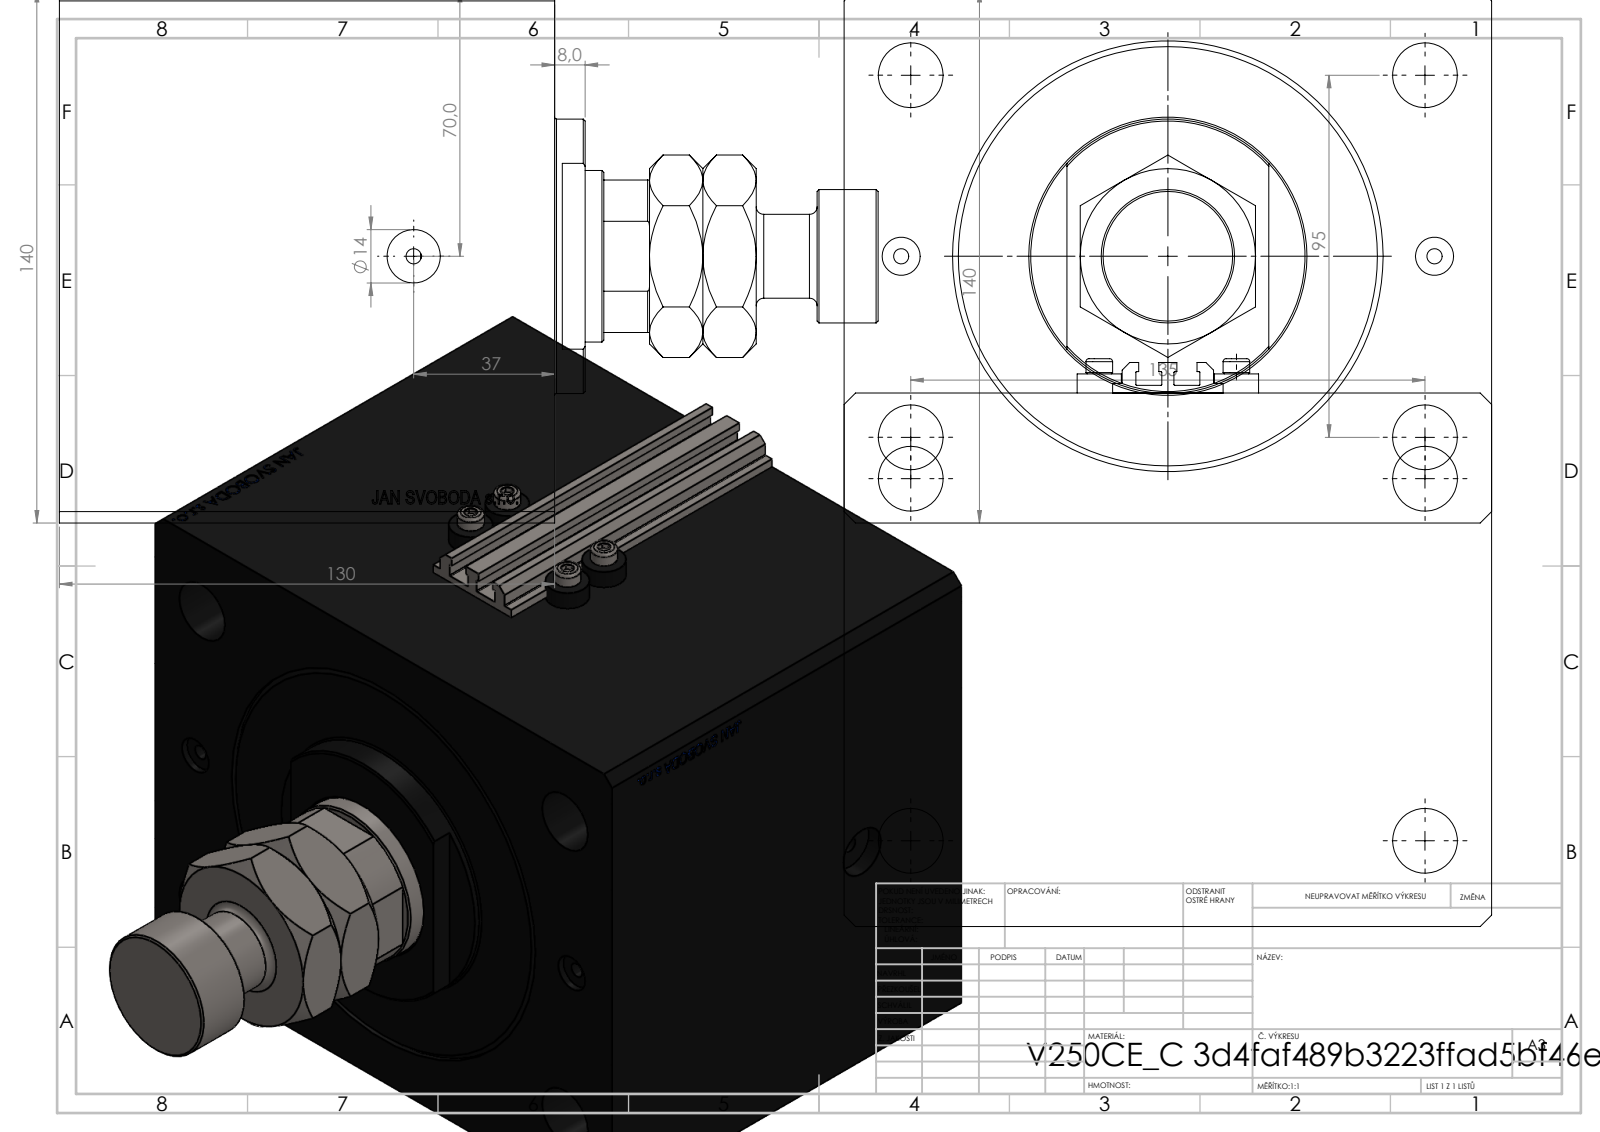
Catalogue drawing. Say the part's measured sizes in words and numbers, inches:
The part is named "V250CE_VC_C; ALLEN BOLT V250CE; V250CE_C_VCP; V250CE_C_Body (+1 more)". Its 3-D file was written by "SolidWorks 2019 (CONFIG_CONTROL_DESIGN)". It is 9 solids with 1086 faces: 520 planar, 90 cylindrical and 476 other. Overall it measures 8.461 by 6.693 by 5.866 inches. Its volume is 179.4 cubic inches and its surface area 459.9 square inches. Round holes: 8 of diameter 0.157, 4 of diameter 0.669, 2 of diameter 0.394, 2 of diameter 0.551, 1 of diameter 1.24, 1 of diameter 1.772, 1 of diameter 3.937, 1 of diameter 4.449. Round bosses or shafts: 4 of diameter 0.457, 4 of diameter 0.276, 1 of diameter 2.835, 1 of diameter 1.378, 1 of diameter 0.866. Partial cylindrical surfaces (rounded edges, fillets, slot ends): 10 of radius 0.008, 1 of radius 0.866. The main face-to-face distances are 5.512, 5.118, 6.693, 1.138, 3.98, 3.736, 2.598, 1.382, 1.811, 2.949. The hole center spacings are 1.873, 3.25, 5.727, 0.535, 1.417, 1.515, 2.756, 3.74.
